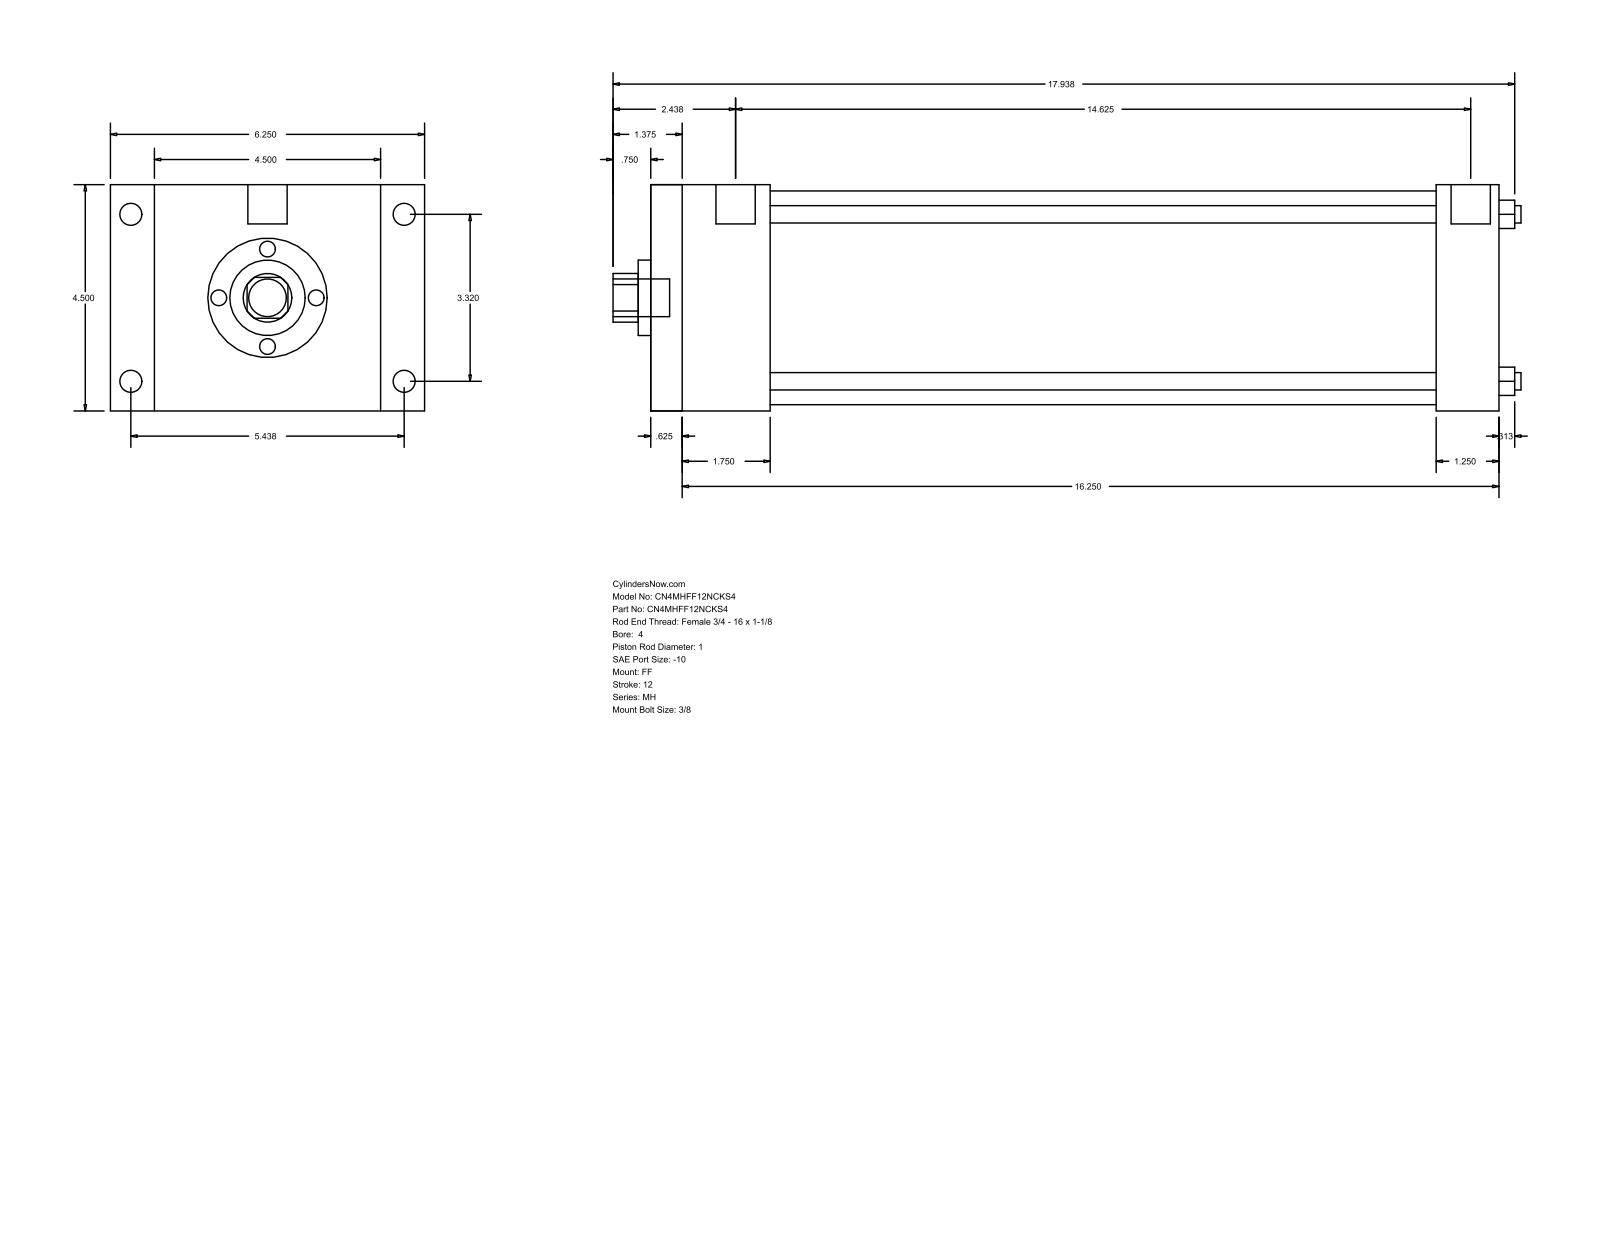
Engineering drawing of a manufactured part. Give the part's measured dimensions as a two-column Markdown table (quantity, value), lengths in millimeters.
| quantity | value |
| --- | --- |
| part name | MH_FF__0400_1 |
| STEP written by | GSSL Pune (CONFIG_CONTROL_DESIGN) |
| units | millimeters |
| bodies | 0 solids, 92 faces (64 planar, 28 cylindrical, 0 other) |
| overall size | 458.79 × 158.75 × 114.3 |
| round holes (diameter × count) | 8.76 × 4, 25.4 × 1, 38.1 × 1, 107.95 × 1 |
| round bosses / shafts (diameter × count) | 11.13 × 4, 8.73 × 4, 19.84 × 2, 19.05 × 1 |
| partial cylindrical surfaces (radius × count) | 12.29 × 1 |
| main face-to-face distances | 114.3, 428.63, 15.87, 412.76, 60.33, 44.46, 368.3, 396.88, 381.01, 336.55 |
| hole center spacings | 59.62, 84.32, 119.25 |
